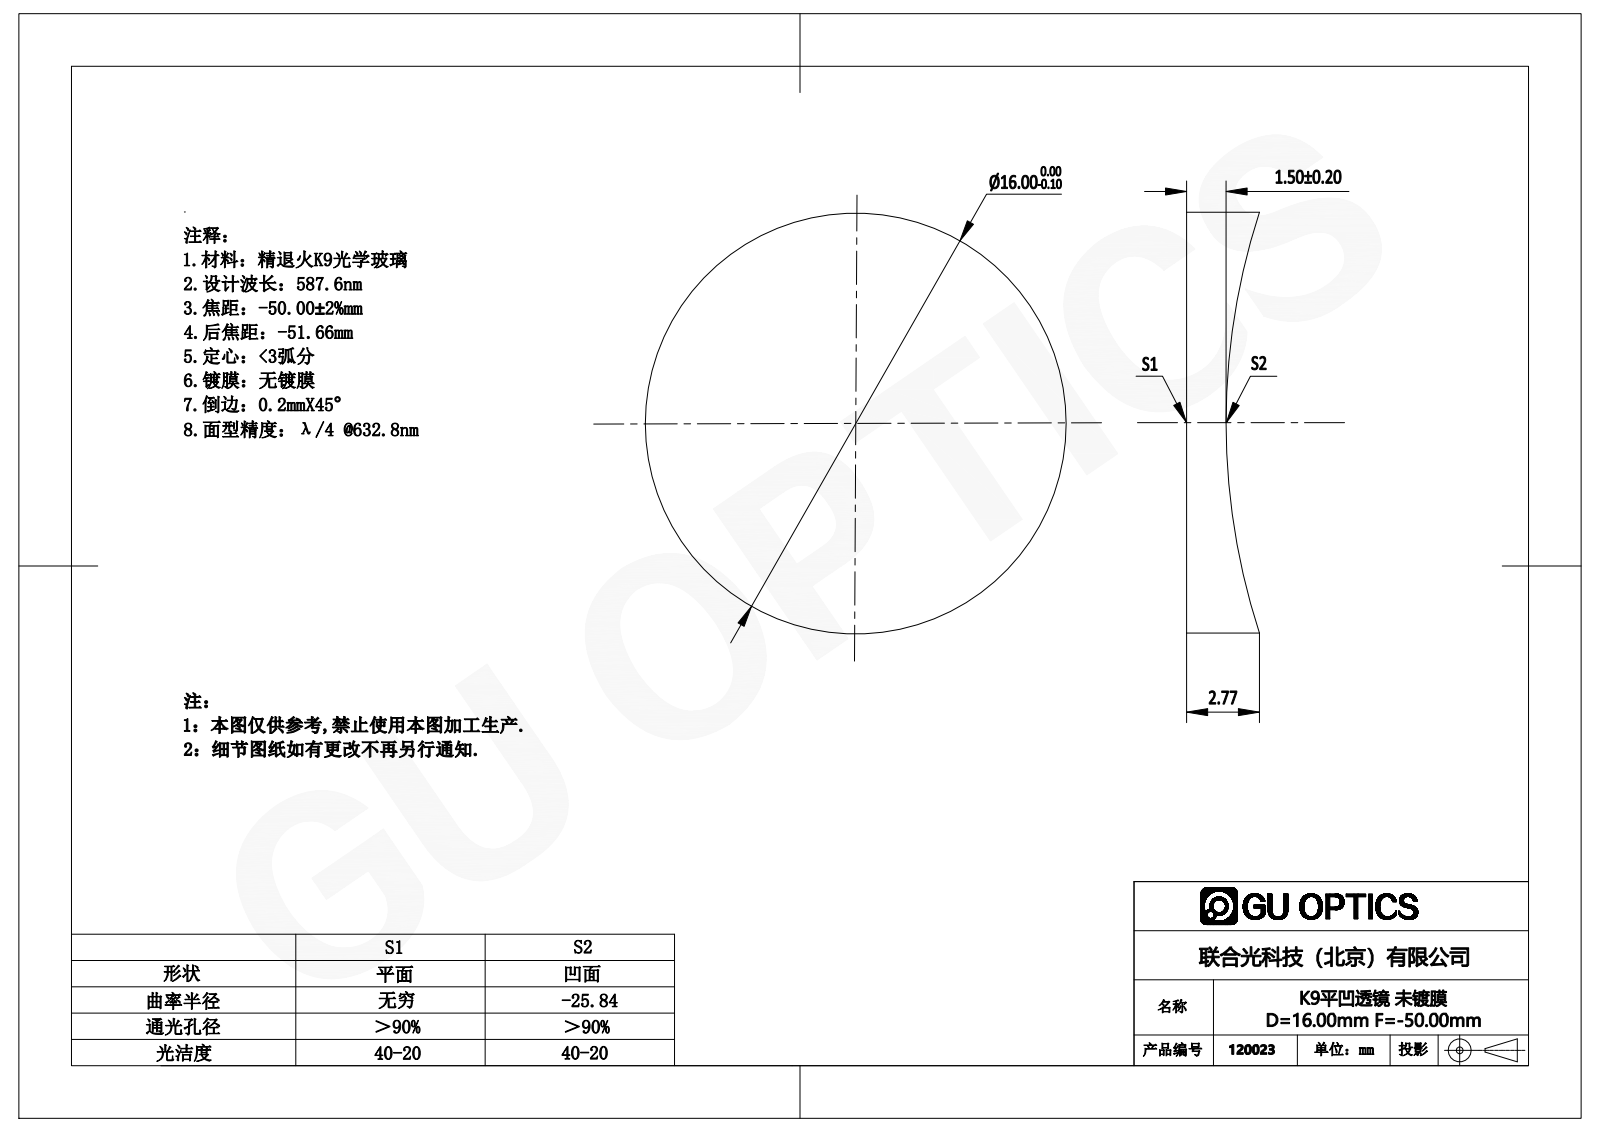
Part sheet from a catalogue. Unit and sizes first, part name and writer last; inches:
Units: inches
Overall size (bounding box): 0.63 × 0.63 × 0.109
Round bosses / shafts (diameter × count): ⌀0.63 ×1
Volume: 0.026 in³ · Surface area: 0.846 in²
Bodies: 1 solid, 5 faces (1 planar, 2 cylindrical, 2 other)
Part name (STEP PRODUCT): 120023
STEP written by: SolidWorks 2016 (AUTOMOTIVE_DESIGN)
